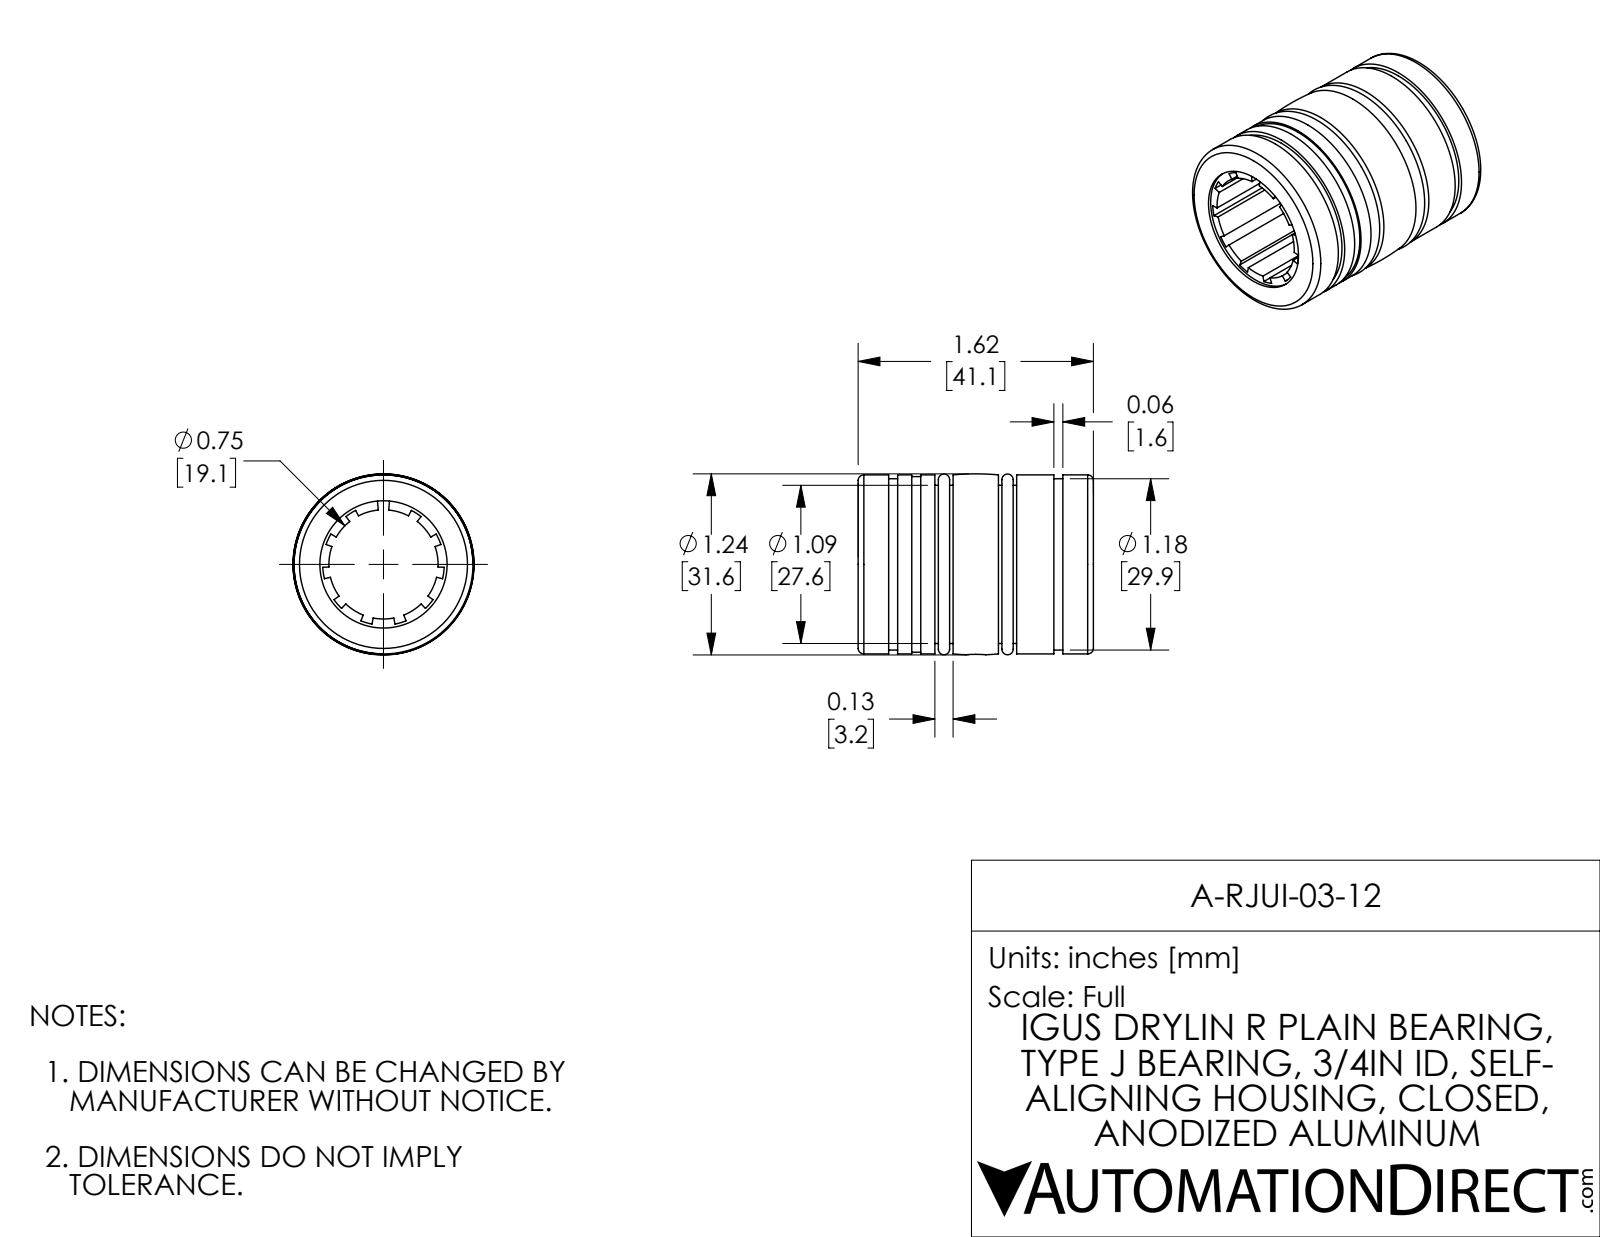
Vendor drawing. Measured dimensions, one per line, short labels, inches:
name: A-RJUI-03-12
written by: SolidWorks 2017 (AUTOMOTIVE_DESIGN)
unit: in
bodies: 4 solids, 161 faces (81 planar, 66 cylindrical, 14 other)
size: 1.617 × 1.244 × 1.244
volume: 1.09 in³; area: 25.24 in²
holes: 1× ⌀0.141, 1× ⌀0.875, 1× ⌀0.953
bosses: 1× ⌀1.23, 1× ⌀1.207, 1× ⌀1.177, 1× ⌀1.087, 1× ⌀0.875, 1× ⌀0.134
rounds: 1× R0.375, 1× R0.418, 1× R0.469
face distances: 0.528, 1.09, 0.653, 0.965, 0.125, 0.437, 0.187, 1.617, 0.715, 0.902
